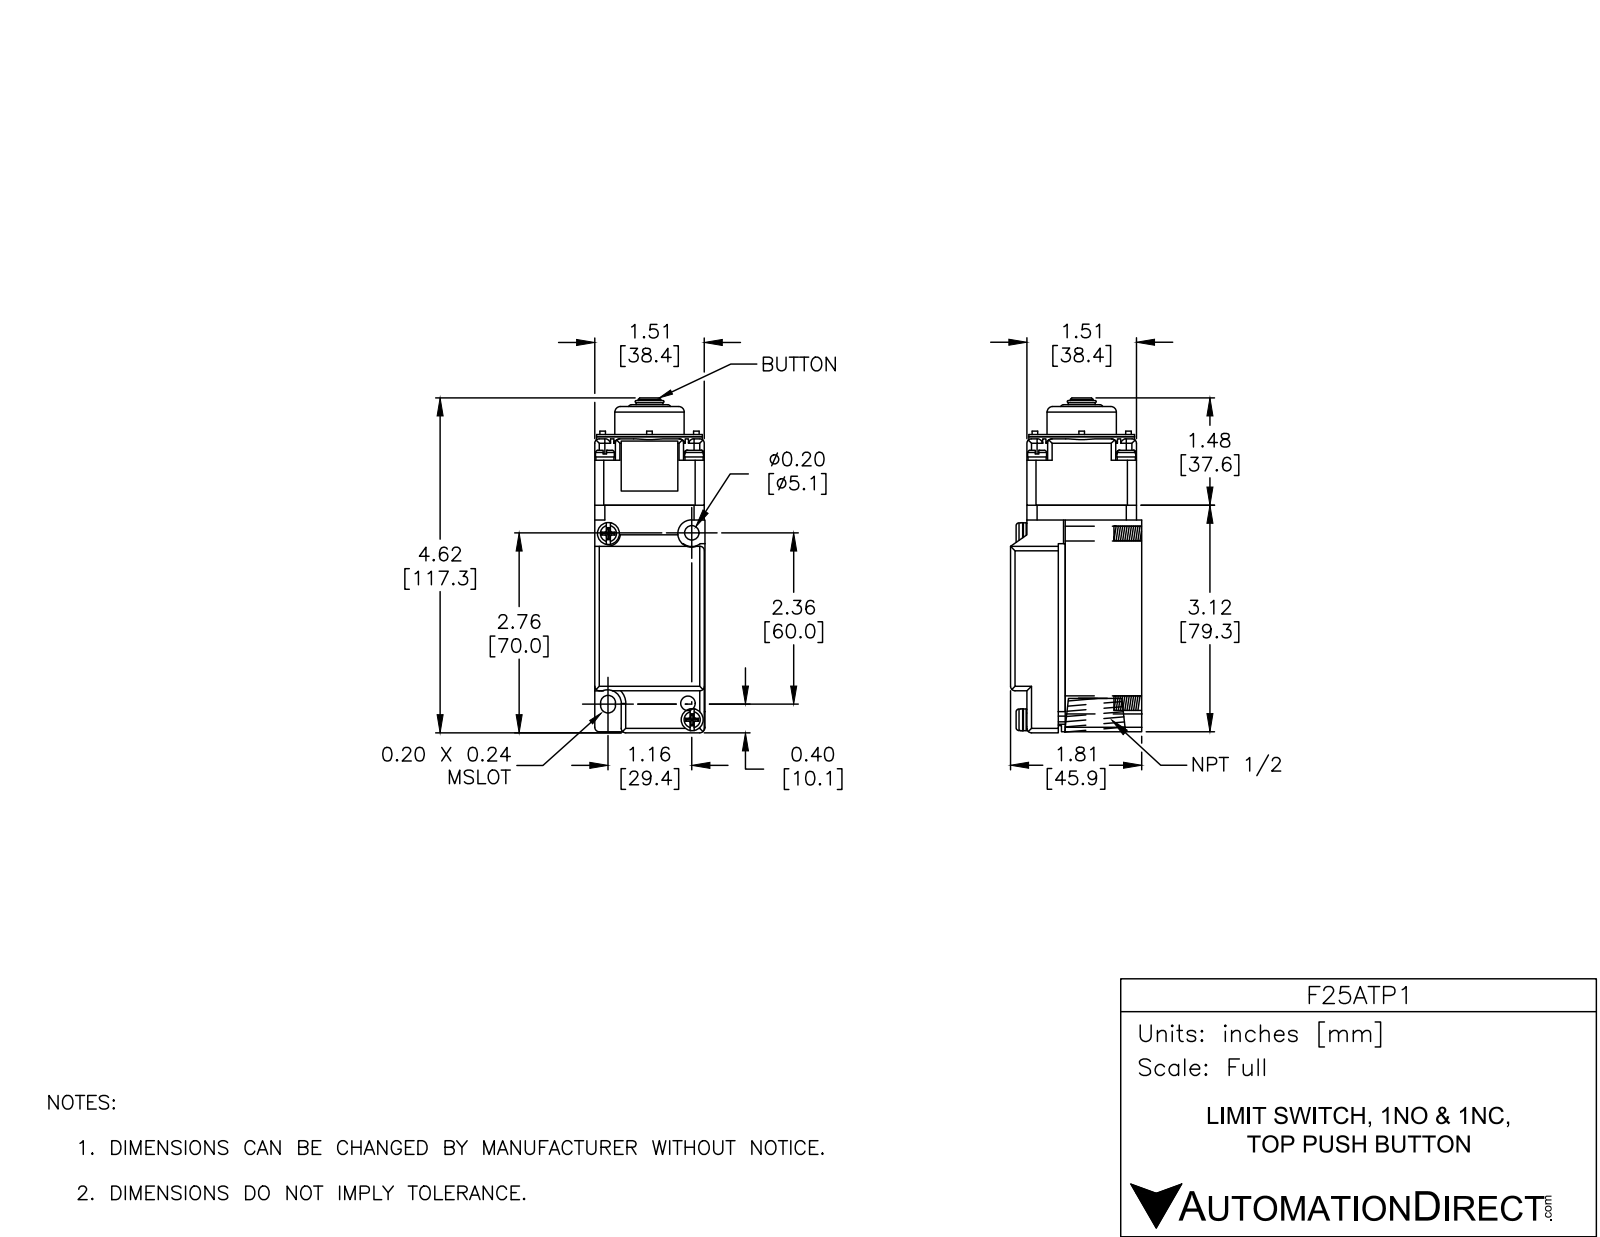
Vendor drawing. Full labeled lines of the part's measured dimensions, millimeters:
Part name (STEP PRODUCT): F25ATP1_A
STEP written by: SolidWorks 2018 (AUTOMOTIVE_DESIGN)
Units: millimetres
Bodies: 12 solids, 616 faces (242 planar, 125 cylindrical, 249 other)
Overall size (bounding box): 117.3 × 45.9 × 38.6
Volume: 161 600 mm³ · Surface area: 45 970 mm²
Round holes (diameter × count): ⌀2 ×4, ⌀4.5 ×4, ⌀4.8 ×3, ⌀5.1 ×3, ⌀5.8 ×1, ⌀23.4 ×1, ⌀26.8 ×1
Round bosses / shafts (diameter × count): ⌀6.4 ×5, ⌀6.6 ×4, ⌀3.6 ×4, ⌀7.7 ×2, ⌀7.6 ×2, ⌀37 ×1, ⌀24.3 ×1, ⌀10.2 ×1
Partial cylindrical surfaces — rounded edges, fillets, slot ends (radius × count): R1.6 ×21, R0.8 ×16, R0.4 ×8, R1.6 ×8, R3.6 ×4, R3.7 ×4, R2.6 ×2, R4.8 ×2
Main face-to-face distances: 2.4, 29.2, 26.8, 38.6, 16.8, 19.2, 45.9, 38.4, 24, 5.8
Hole centre spacings: 35.6, 15.6, 16.4, 15.6, 22.1, 22.1, 23.2, 23.2
